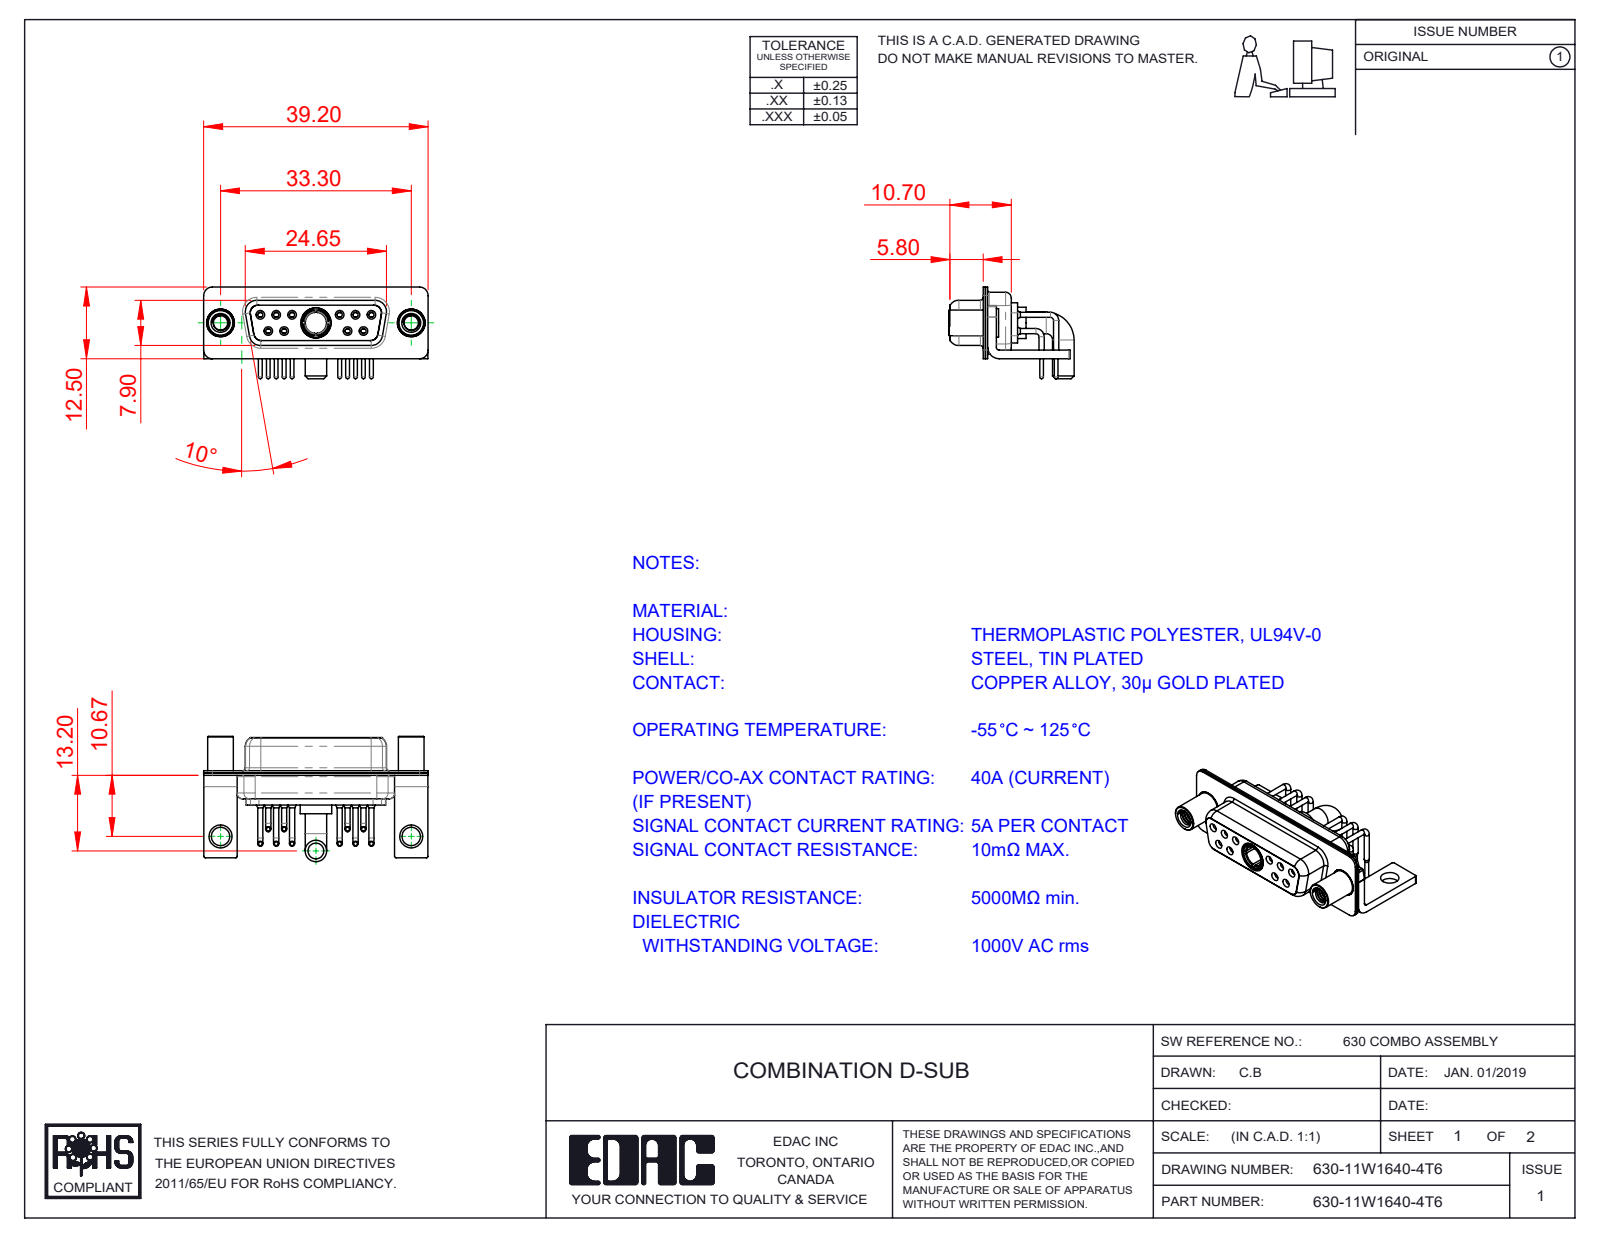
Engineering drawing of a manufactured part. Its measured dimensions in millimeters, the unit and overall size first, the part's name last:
Units: millimetres
Overall size (bounding box): 39.2 × 21.88 × 16
Round holes (diameter × count): ⌀0.9 ×10, ⌀1.1 ×10, ⌀1.5 ×10, ⌀2 ×10, ⌀1.7 ×6, ⌀1.6 ×4, ⌀4.85 ×3, ⌀2.5 ×2, ⌀3.2 ×2, ⌀4 ×2, ⌀4.05 ×2, ⌀3.7 ×1
Round bosses / shafts (diameter × count): ⌀0.9 ×10, ⌀0.65 ×10, ⌀1.6 ×6, ⌀5 ×2, ⌀4.95 ×2, ⌀4.8 ×2, ⌀4.5 ×2, ⌀3.75 ×2
Partial cylindrical surfaces — rounded edges, fillets, slot ends (radius × count): R0.25 ×16, R1.5 ×16, R2 ×13, R1.35 ×12, R1.6 ×8, R0.5 ×5, R0.6 ×4, R0.65 ×4
Main face-to-face distances: 0.4, 0.8, 1.4, 0.45, 8.45, 1.5, 1.8, 8.9, 6.2, 2.3
Hole centre spacings: 3.16, 2.77, 13.85, 11.08, 16.62, 5.03, 5.04, 5.54
Volume: 3 103 mm³ · Surface area: 7 240 mm²
Bodies: 19 solids, 985 faces (268 planar, 464 cylindrical, 253 other)
Part name (STEP PRODUCT): 630Combo Stabilizer Bracket; 630-11W1640-4T6; Power Socket_40A RA; 630Combo Housing_11W1 (+5 more)
STEP written by: SolidWorks 2020 (CONFIG_CONTROL_DESIGN)
